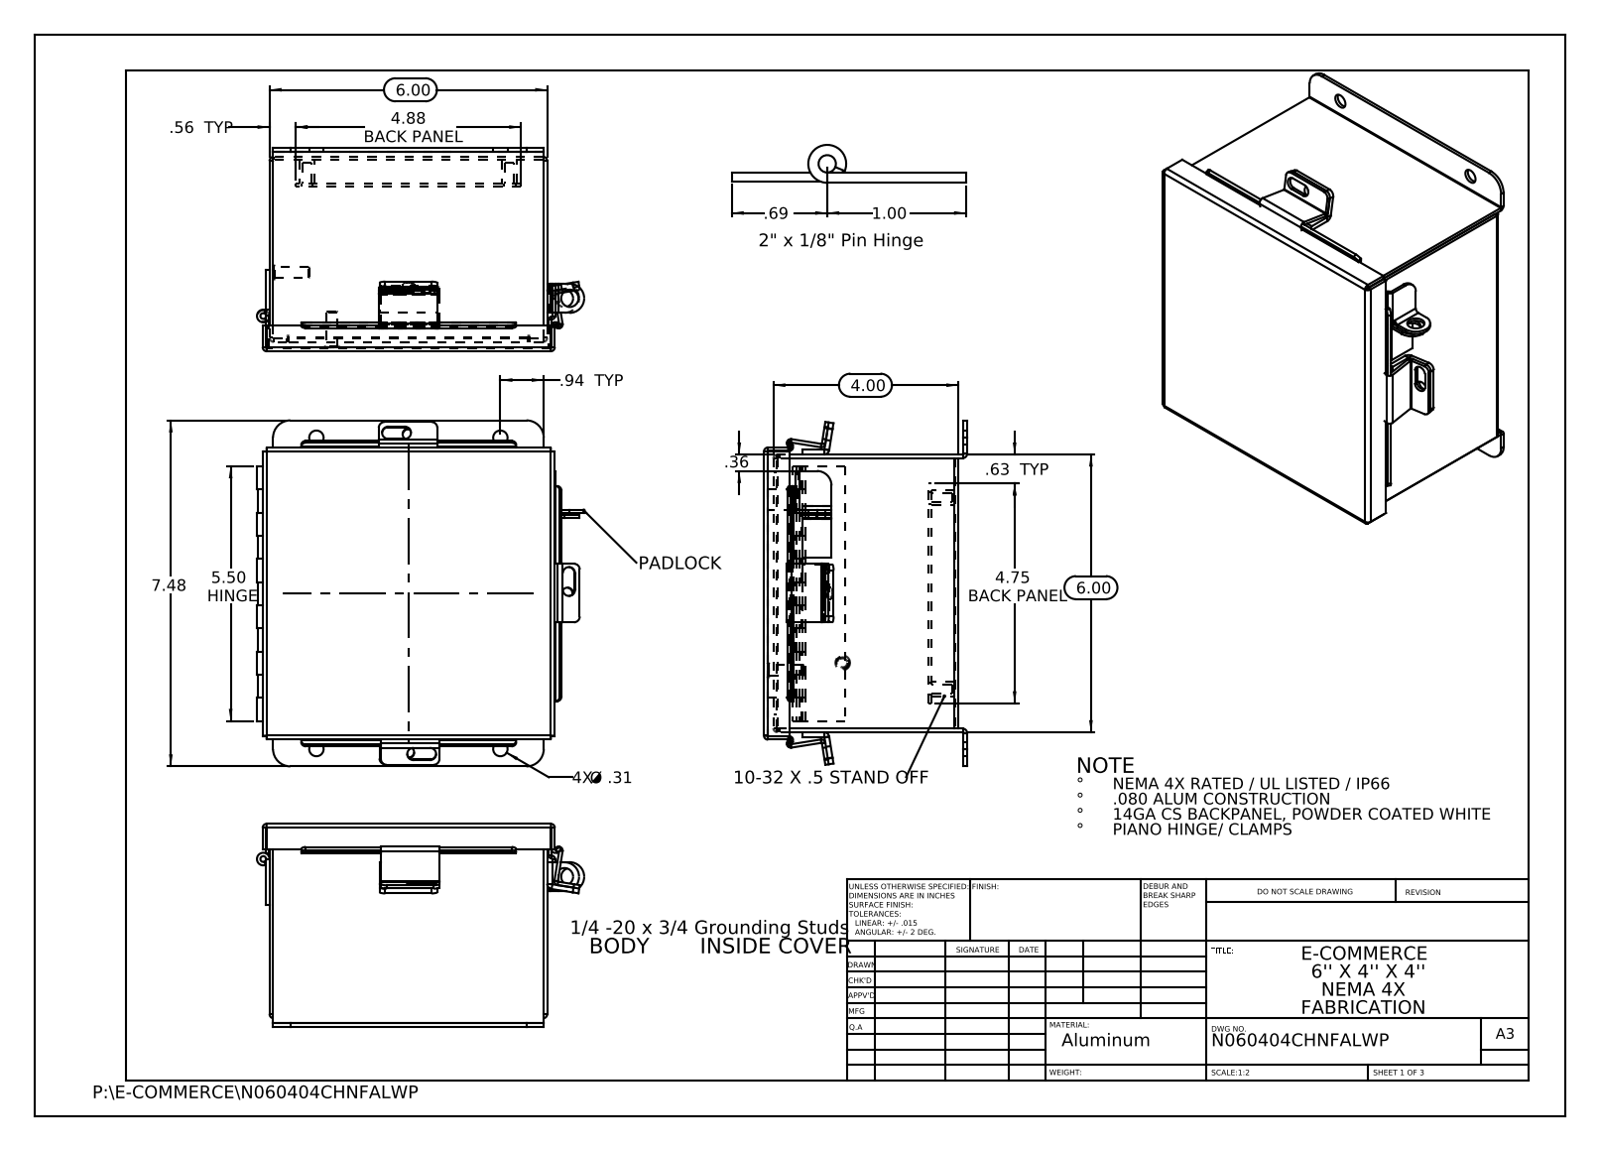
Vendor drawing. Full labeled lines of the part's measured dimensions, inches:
Part name (STEP PRODUCT): N060404CHNFALWP JIC Cover Clamp; N060404CHNFALWP JIC Clamp Bracket; N060404CHNFALWP JIC Backpanel; N060404CHNFALWP JIC_Standoff (+8 more)
STEP written by: SolidWorks 2013 (CONFIG_CONTROL_DESIGN)
Units: inches
Bodies: 21 solids, 548 faces (343 planar, 185 cylindrical, 20 other)
Overall size (bounding box): 7.476 × 7.072 × 4.39
Volume: 18.33 in³ · Surface area: 507.2 in²
Round holes (diameter × count): ⌀0.25 ×7, ⌀0.187 ×4, ⌀0.312 ×4, ⌀0.125 ×1, ⌀0.125 ×1, ⌀0.373 ×1, ⌀0.375 ×1
Round bosses / shafts (diameter × count): ⌀0.313 ×4, ⌀0.315 ×2, ⌀0.236 ×2, ⌀0.273 ×1, ⌀0.25 ×1
Partial cylindrical surfaces — rounded edges, fillets, slot ends (radius × count): R0.013 ×13, R0.009 ×12, R0.088 ×12, R0.125 ×10, R0.083 ×6, R0.1 ×6, R0.133 ×6, R0.375 ×4
Main face-to-face distances: 0.075, 5.925, 4.128, 5.85, 6, 4.053, 4.203, 0.074, 0.575, 0.5
Hole centre spacings: 1.315, 4.373, 5.43, 6.846, 3.976, 4.126, 4.375, 6.013
